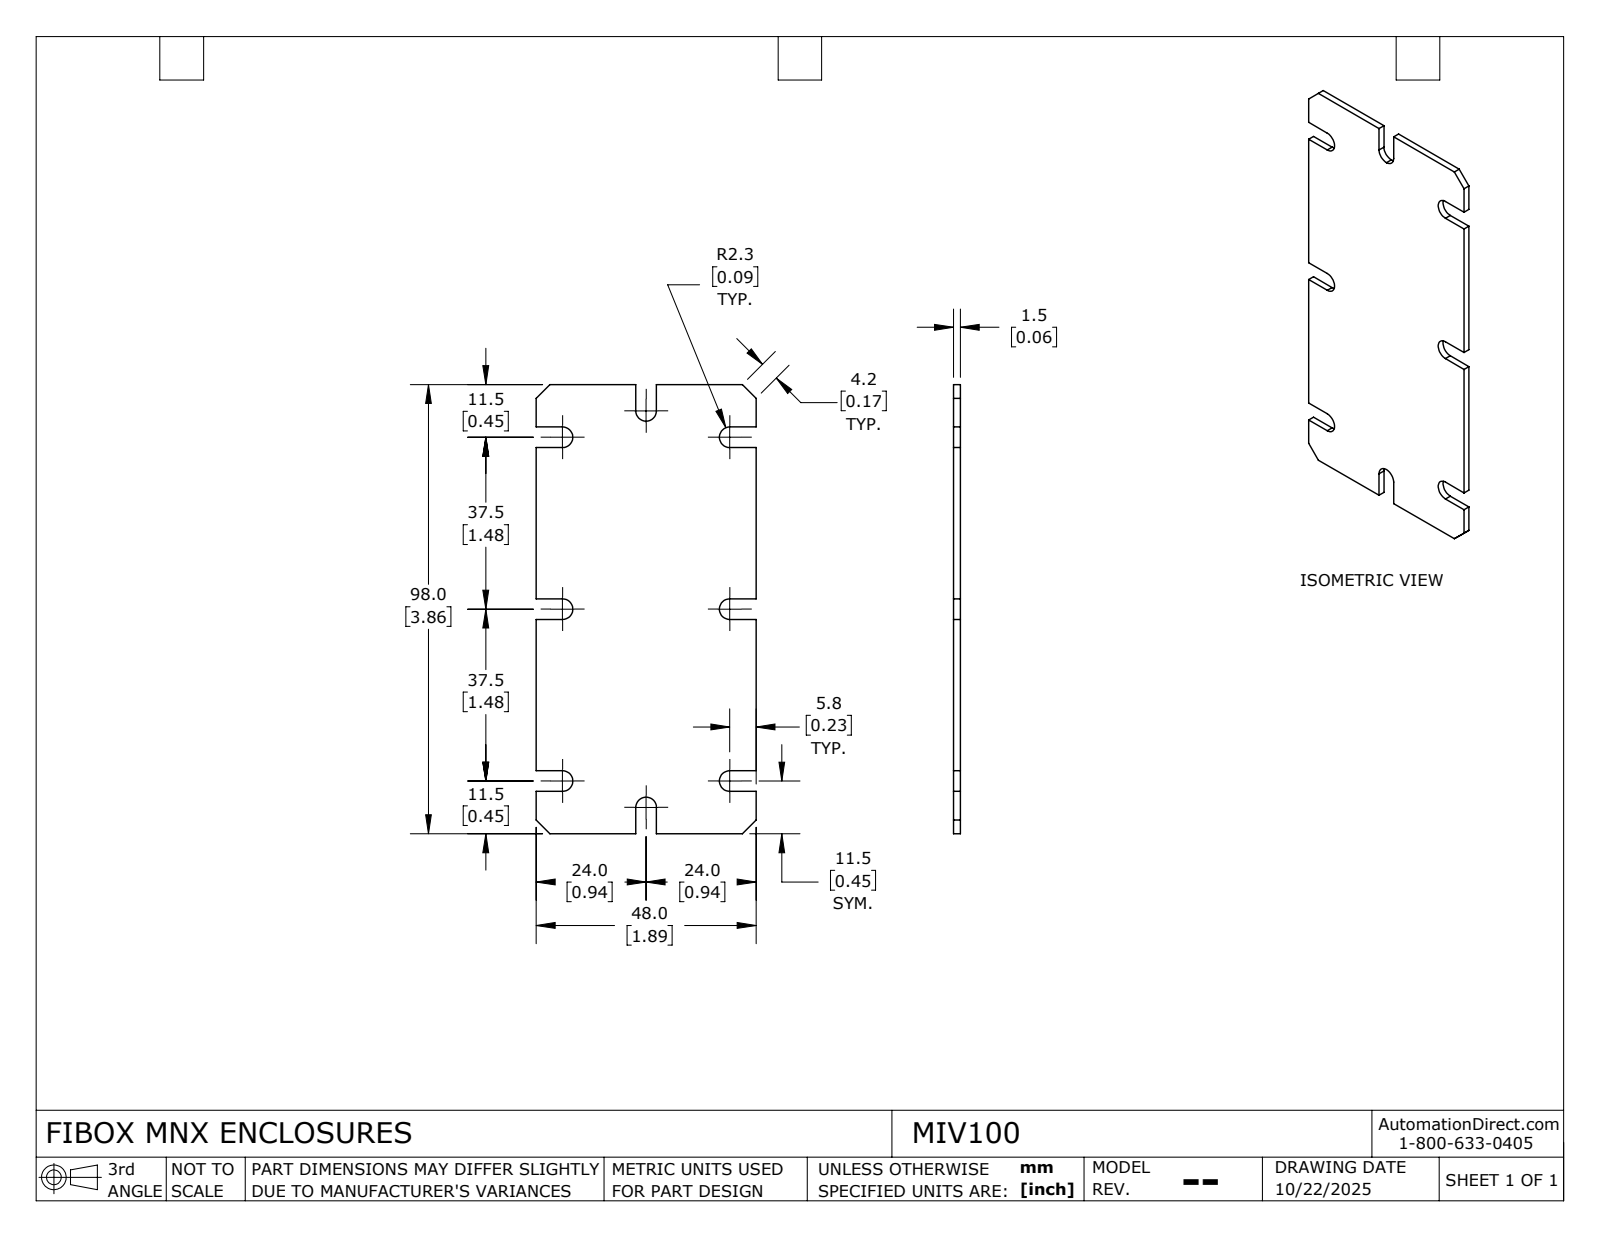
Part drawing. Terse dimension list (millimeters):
name: MIV_100_Default
written by: SolidWorks 2024 (CONFIG_CONTROL_DESIGN)
unit: mm
bodies: 1 solid, 43 faces (34 planar, 9 cylindrical, 0 other)
size: 98 × 48 × 1.5
volume: 6 623 mm³; area: 9 427 mm²
rounds: 8× R2.25
face distances: 1.5, 48, 4.5, 37.5, 98, 21.75, 26.25, 9.25, 13.75, 46.75
